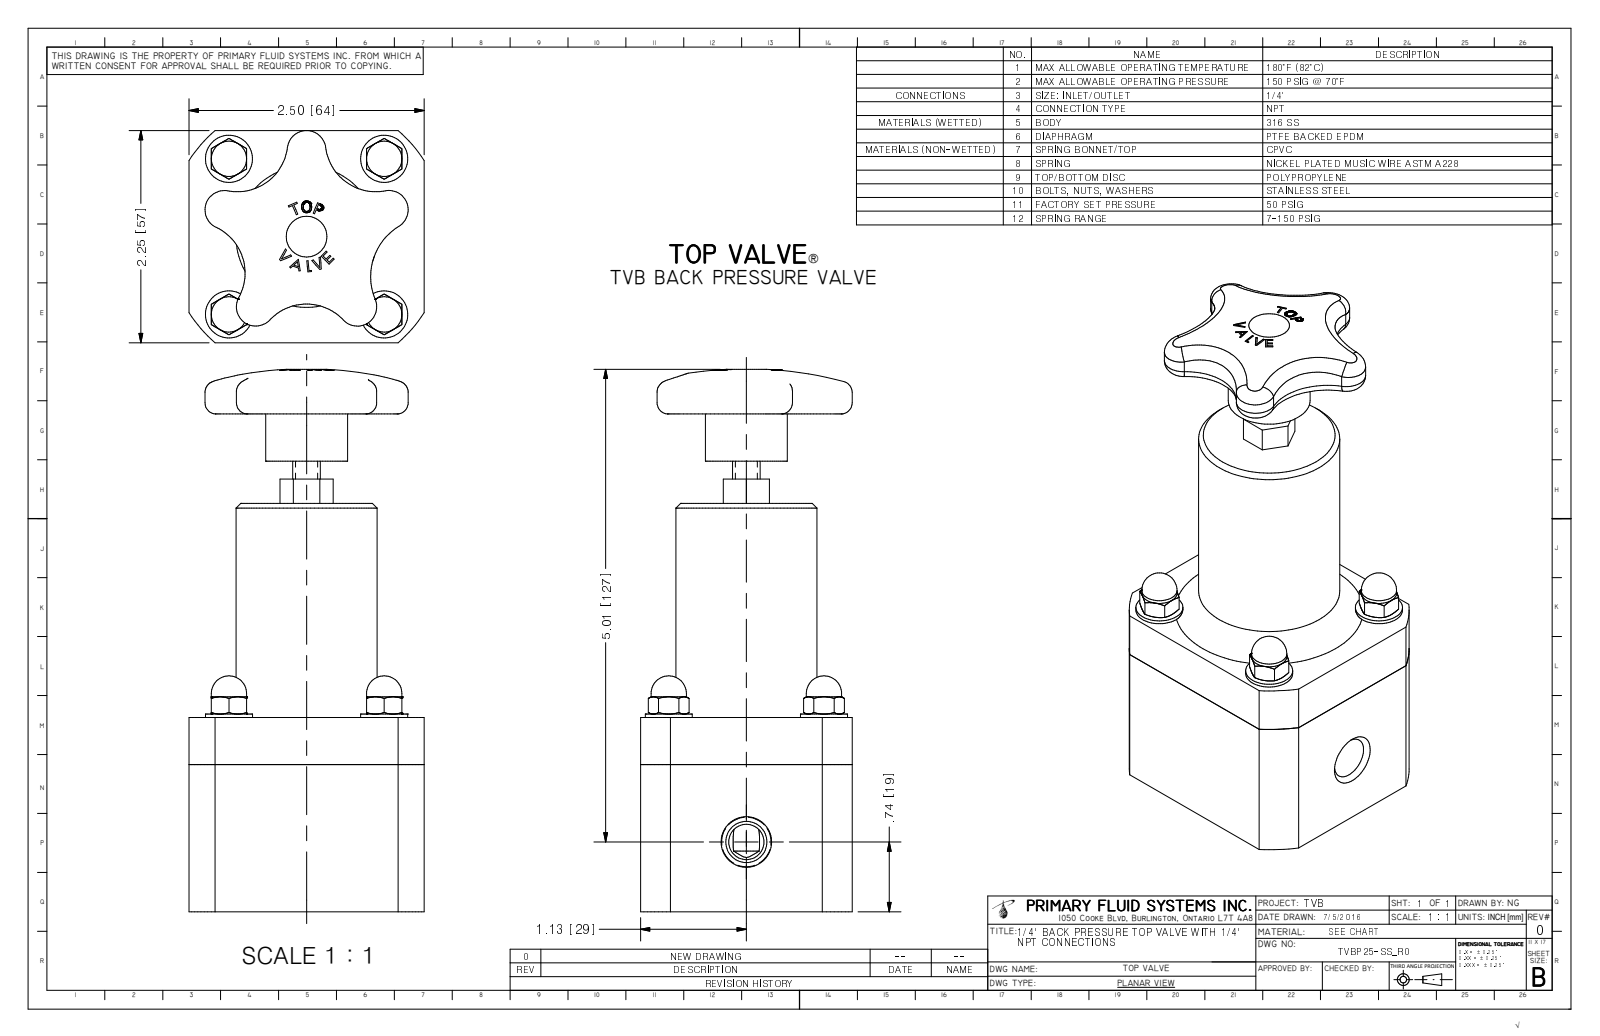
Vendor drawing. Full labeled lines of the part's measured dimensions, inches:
Part name (STEP PRODUCT): TVBP25-SS-R0
STEP written by: Autodesk Inventor 2009 (AUTOMOTIVE_DESIGN)
Units: inches
Bodies: 1 solid, 337 faces (140 planar, 45 cylindrical, 152 other)
Overall size (bounding box): 5.752 × 2.5 × 2.25
Volume: 16.48 in³ · Surface area: 55.22 in²
Round holes (diameter × count): ⌀0.147 ×4, ⌀0.437 ×1
Round bosses / shafts (diameter × count): ⌀0.5 ×4, ⌀0.375 ×4, ⌀0.312 ×4, ⌀1.5 ×1, ⌀0.87 ×1, ⌀0.293 ×1
Partial cylindrical surfaces — rounded edges, fillets, slot ends (radius × count): R0.085 ×5, R0.205 ×5, R0.536 ×4, R0.656 ×4, R0.625 ×1, R0.745 ×1, R1.488 ×1
Main face-to-face distances: 2.25, 2.5, 2.06, 4.33, 2.27, 4.778, 2.718, 0.448, 2.096, 0.036
Hole centre spacings: 1.65, 2.333
